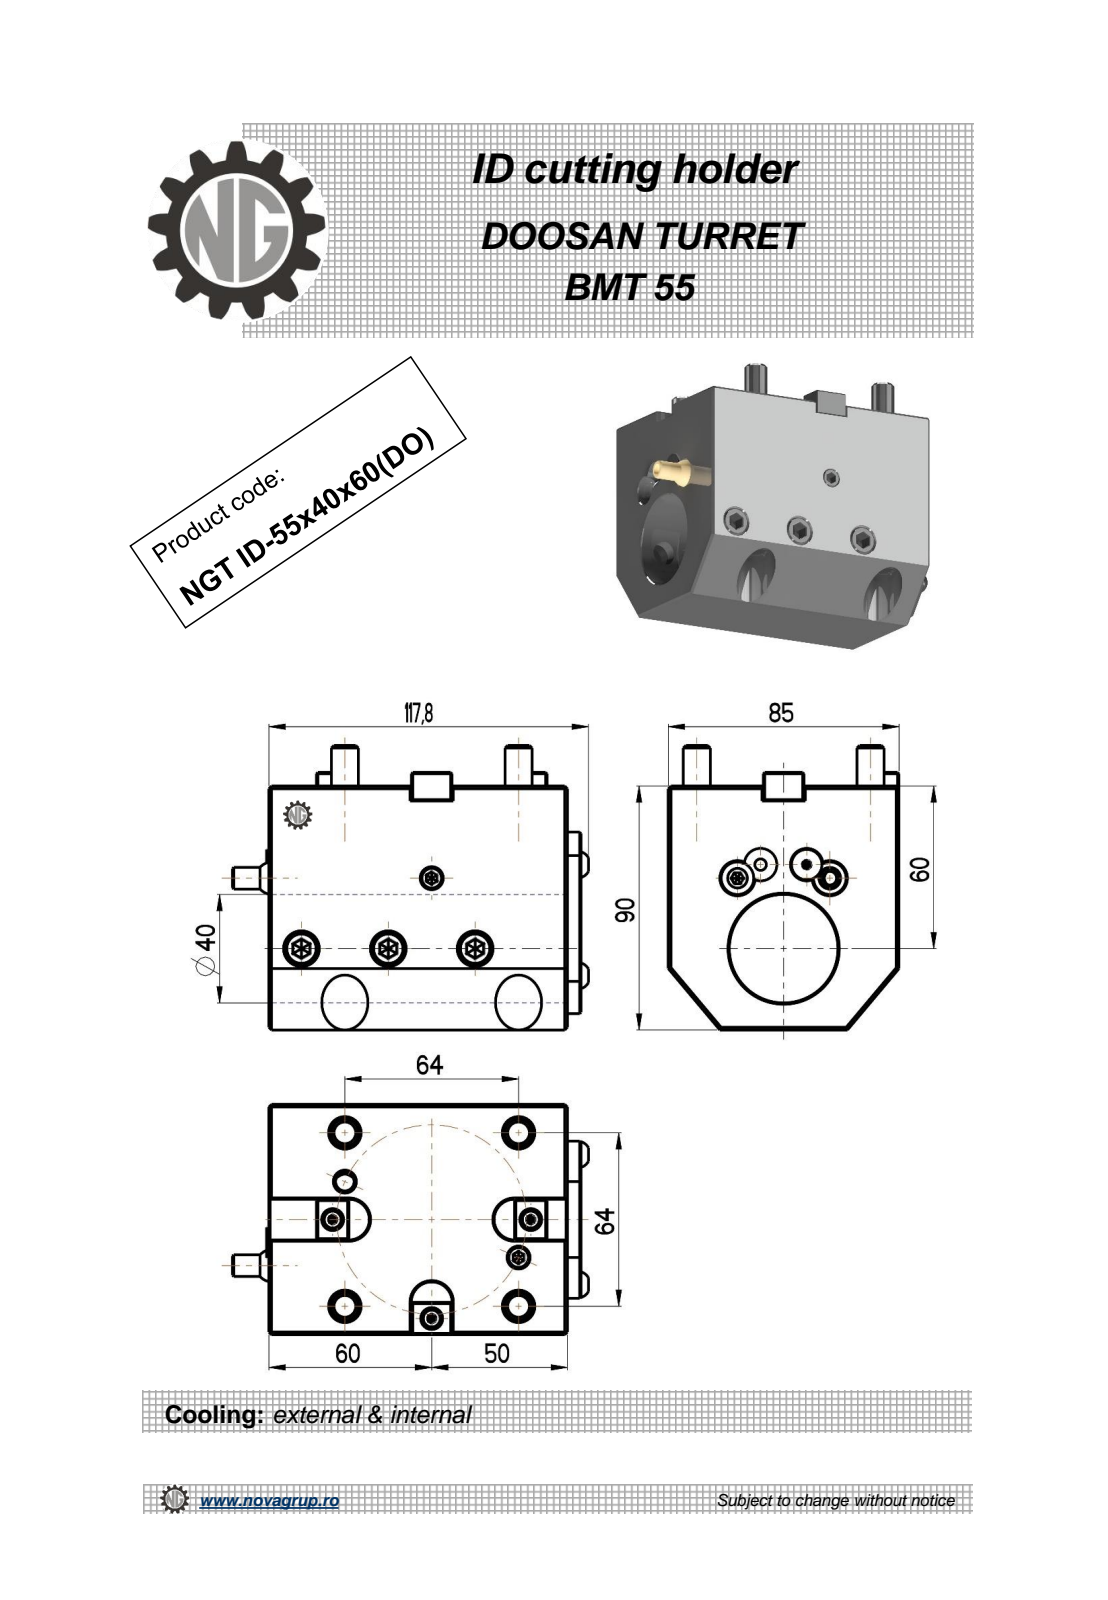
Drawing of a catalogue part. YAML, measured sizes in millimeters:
part_name: "NGT_ID_55_40_60_DO"
step_written_by: "PRO/ENGINEER BY PARAMETRIC TECHNOLOGY CORPORATION, 2010280 (CONFIG_CONTROL_DESIGN)"
units: millimeters
bodies: {solids: 1, faces: 390, planar: 212, cylindrical: 80, other: 98}
overall_size: [130.28, 105, 85]
volume: 672733
surface_area: 72003
round_holes:
  - {diameter: 10.2, count: 3}
  - {diameter: 5, count: 1}
  - {diameter: 6.8, count: 1}
  - {diameter: 40, count: 1}
round_bosses_or_shafts:
  - {diameter: 10, count: 4}
  - {diameter: 11.2, count: 1}
  - {diameter: 8, count: 1}
partial_cylinders:
  - {radius: 0.61, count: 36}
  - {radius: 0.22, count: 6}
  - {radius: 0.41, count: 6}
  - {radius: 7.5, count: 3}
face_to_face_distances: [85, 90, 110, 5, 115, 16, 35, 10, 50, 73]
hole_center_spacings: [32, 64]
